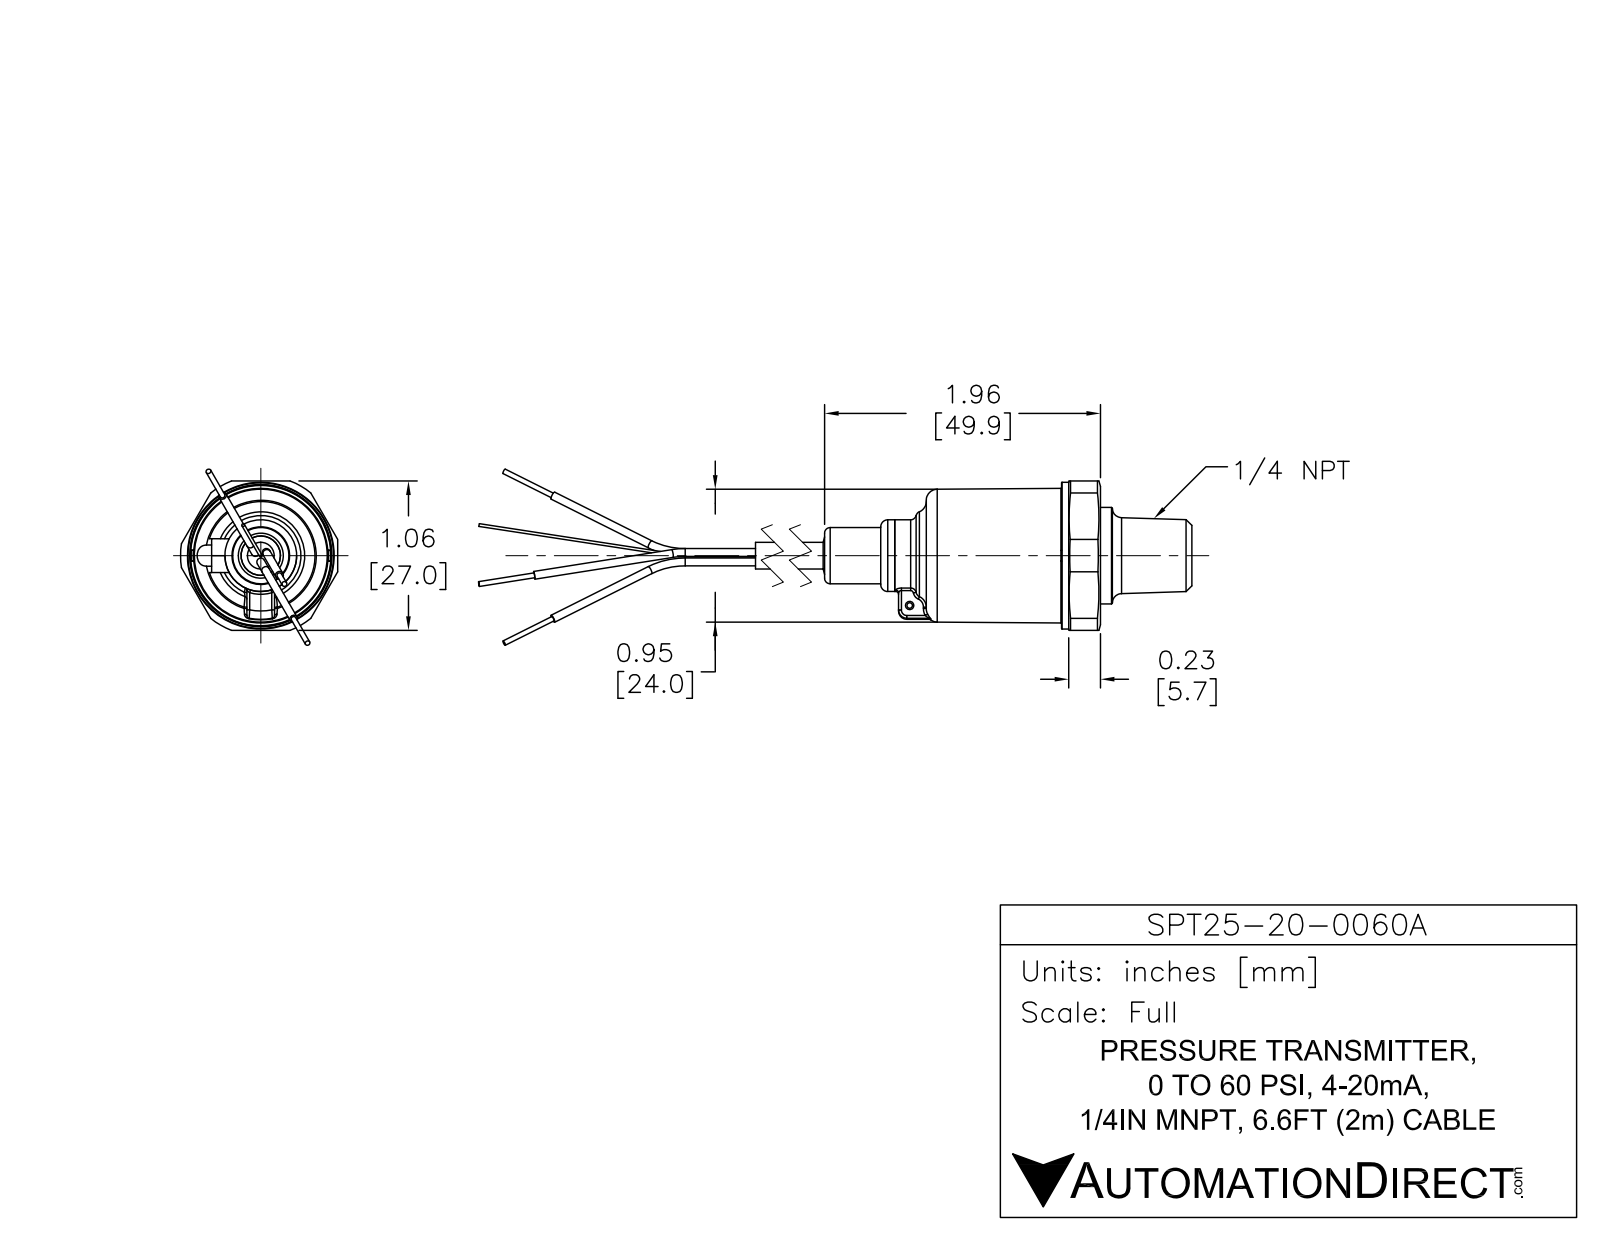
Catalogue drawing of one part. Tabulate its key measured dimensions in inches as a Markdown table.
| quantity | value |
| --- | --- |
| part name | SPT25-20-0060A |
| STEP written by | SolidWorks 2017 (AUTOMOTIVE_DESIGN) |
| units | inches |
| bodies | 7 solids, 116 faces (32 planar, 49 cylindrical, 35 other) |
| overall size | 6.035 × 1.142 × 1.067 |
| volume | 1.269 in³ |
| surface area | 11.11 in² |
| round holes (diameter × count) | 0.039 × 1, 0.13 × 1 |
| round bosses / shafts (diameter × count) | 0.055 × 6, 0.03 × 5, 1.053 × 1, 0.945 × 1, 0.689 × 1, 0.551 × 1, 0.512 × 1, 0.394 × 1 |
| partial cylindrical surfaces (radius × count) | 0.079 × 1, 0.571 × 1 |
| main face-to-face distances | 0.266, 0.945, 0.679, 1.683, 1.949, 2.628, 1.732, 0.049, 0.217, 0.896 |
